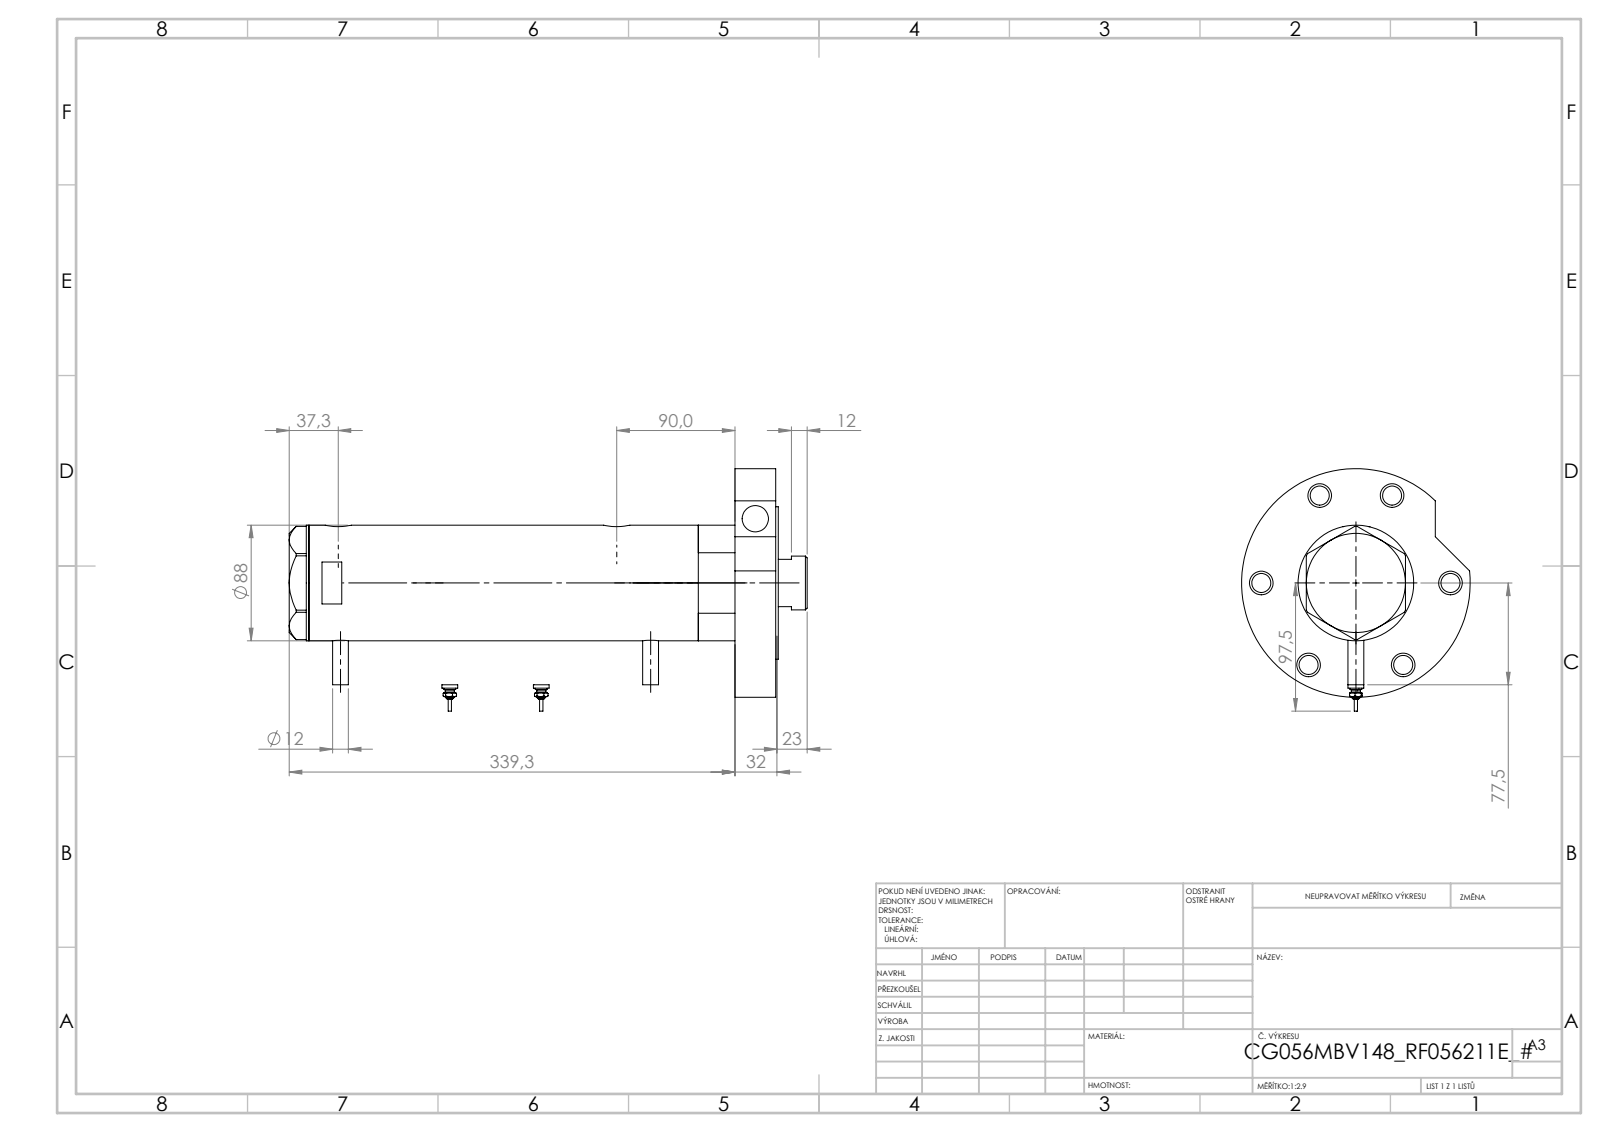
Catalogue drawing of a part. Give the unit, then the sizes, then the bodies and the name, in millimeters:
Units: millimetres
Overall size (bounding box): 394.3 × 184.5 × 174
Round holes (diameter × count): ⌀14.5 ×7, ⌀18 ×6, ⌀20 ×3, ⌀12.5 ×2, ⌀13.16 ×2, ⌀42 ×1, ⌀43.5 ×1, ⌀56 ×1, ⌀60 ×1, ⌀75 ×1, ⌀80 ×1
Round bosses / shafts (diameter × count): ⌀12 ×4, ⌀9 ×2, ⌀7 ×2, ⌀4.5 ×2, ⌀2.5 ×2, ⌀174 ×1, ⌀116 ×1, ⌀88 ×1
Main face-to-face distances: 31, 2, 357.3, 324.3, 355.3, 33, 234.4, 89.9, 120.9, 122.9
Hole centre spacings: 72, 80, 119.73, 124.71, 129.15, 143.69, 1.7, 25.8
Volume: 2 563 000 mm³ · Surface area: 360 779 mm²
Bodies: 7 solids, 257 faces (91 planar, 102 cylindrical, 64 other)
Part name (STEP PRODUCT): V270CG_RF211E; Switch; V270CG_FRONT; V270CG_VC (+2 more)
STEP written by: SolidWorks 2019 (CONFIG_CONTROL_DESIGN)
